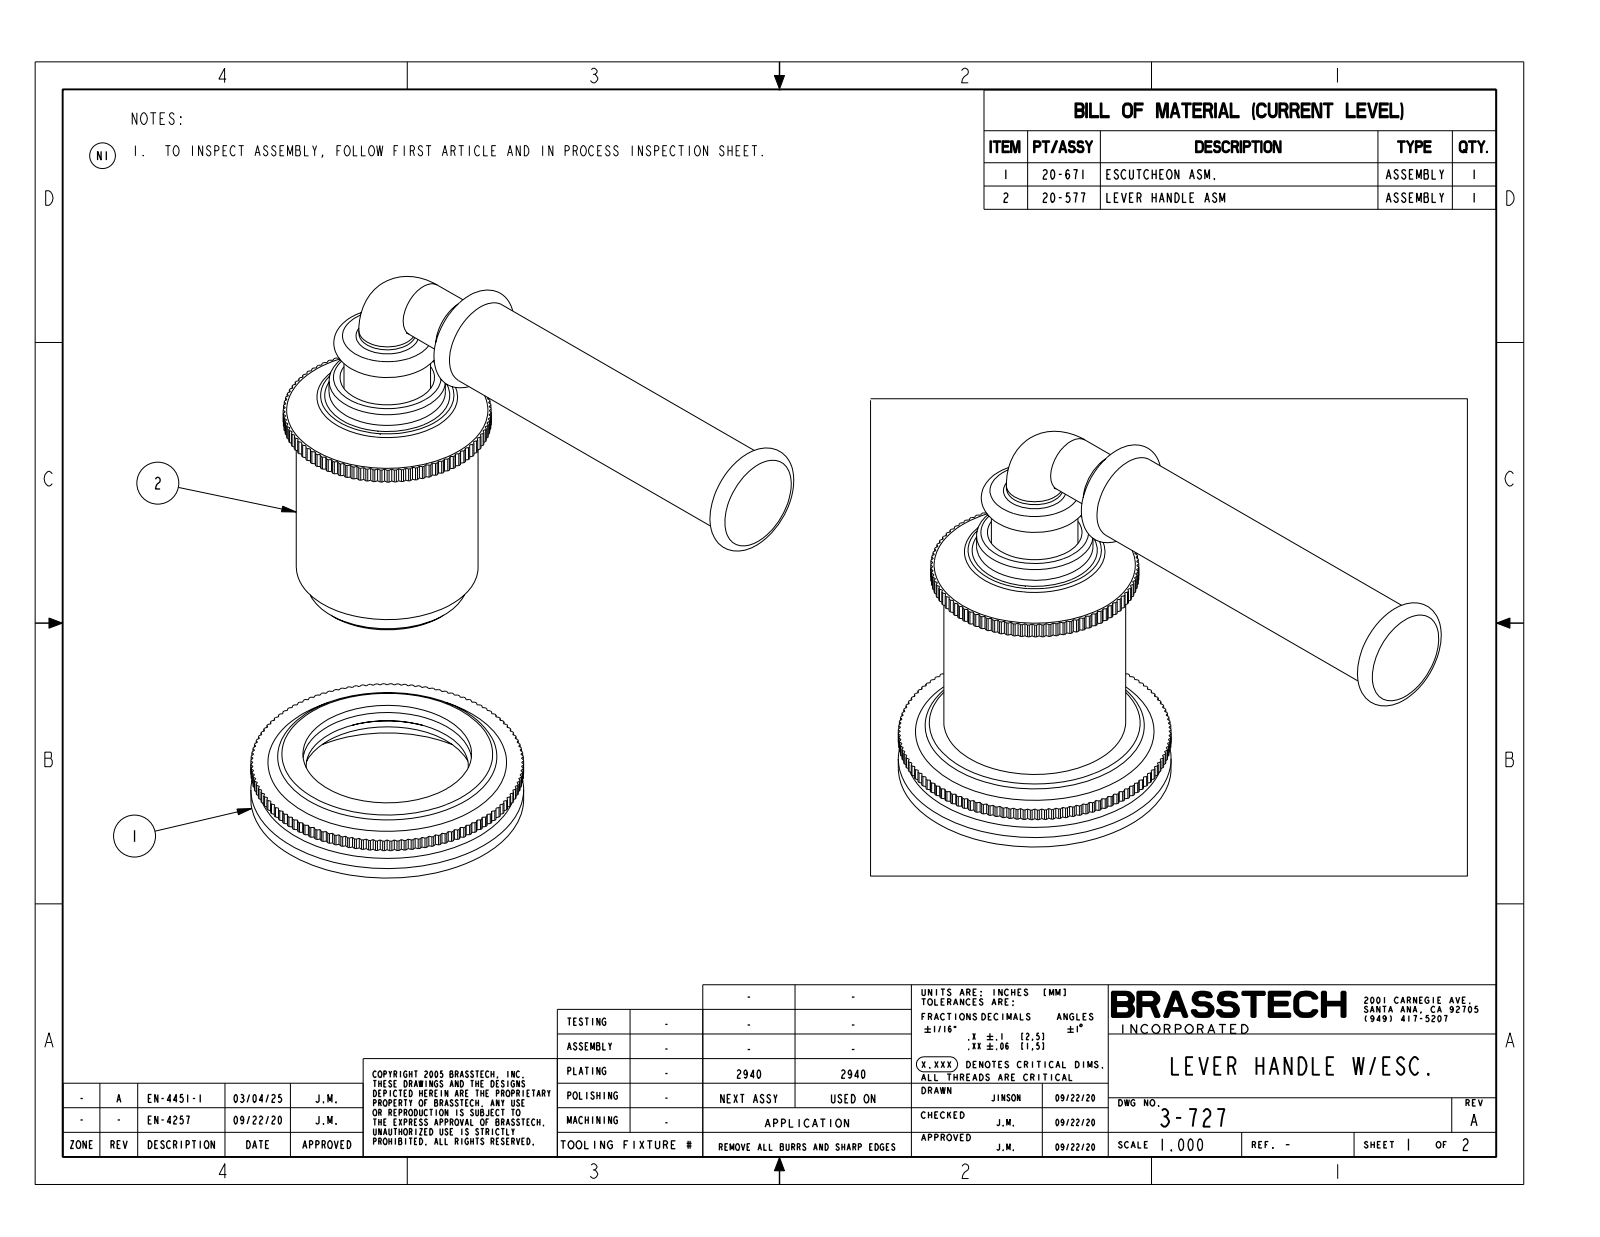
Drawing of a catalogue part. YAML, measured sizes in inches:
part_name: "3-727"
step_written_by: "CREO PARAMETRIC BY PTC INC, 2019352 (CONFIG_CONTROL_DESIGN)"
units: inches
bodies: {solids: 1, faces: 695, planar: 436, cylindrical: 231, other: 28}
overall_size: [4.555, 3.114, 1.9]
volume: 3.898
surface_area: 23.09
round_holes:
  - {diameter: 0.41, count: 1}
round_bosses_or_shafts:
  - {diameter: 0.39, count: 2}
  - {diameter: 1.9, count: 1}
  - {diameter: 1.8, count: 1}
  - {diameter: 1.25, count: 1}
  - {diameter: 1.2, count: 1}
  - {diameter: 0.8, count: 1}
  - {diameter: 0.6, count: 1}
  - {diameter: 0.595, count: 1}
partial_cylinders:
  - {radius: 0.715, count: 1}
face_to_face_distances: [0.31, 0.38, 0.07, 1.61, 1.3, 1.23, 0.15, 0.23, 0.08, 1.38]
